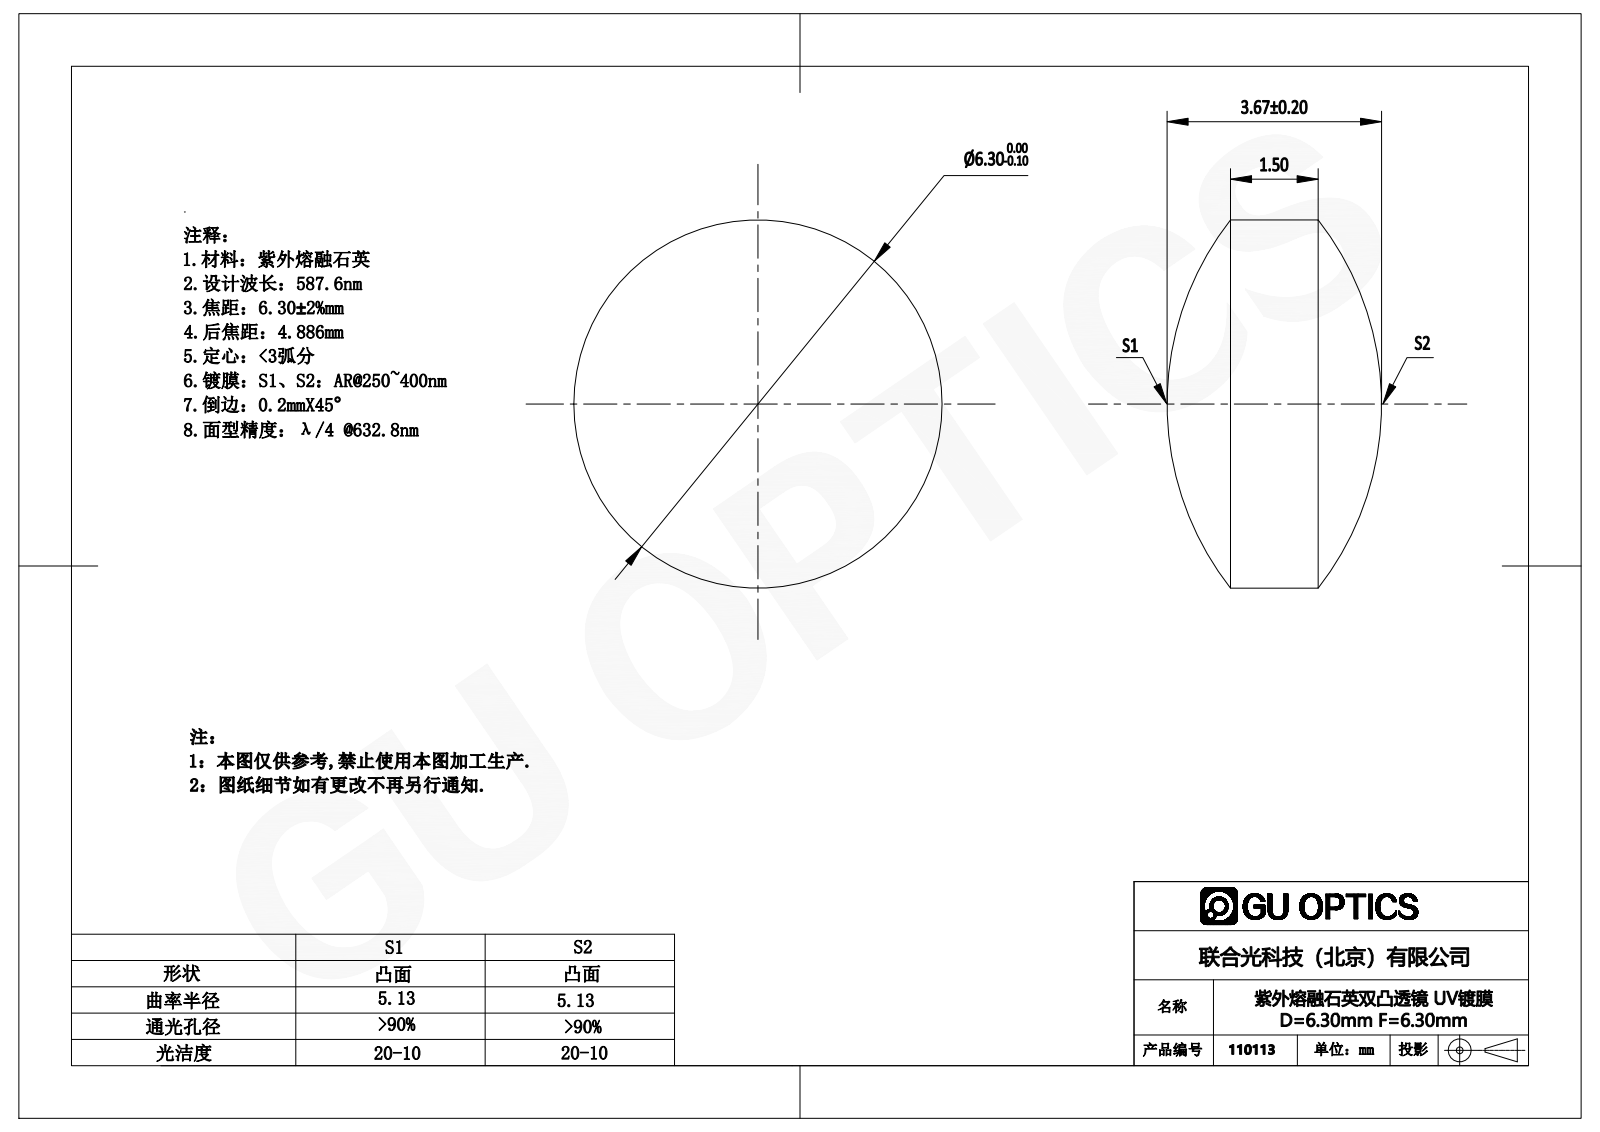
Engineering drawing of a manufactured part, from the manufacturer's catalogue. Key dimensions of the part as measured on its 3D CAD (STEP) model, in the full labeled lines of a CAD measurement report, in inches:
Part name (STEP PRODUCT): 110089
STEP written by: SolidWorks 2016 (CONFIG_CONTROL_DESIGN)
Units: inches
Bodies: 1 solid, 6 faces (0 planar, 2 cylindrical, 4 other)
Overall size (bounding box): 0.248 × 0.248 × 0.144
Volume: 0.005 in³ · Surface area: 0.15 in²
Round bosses / shafts (diameter × count): ⌀0.248 ×1
